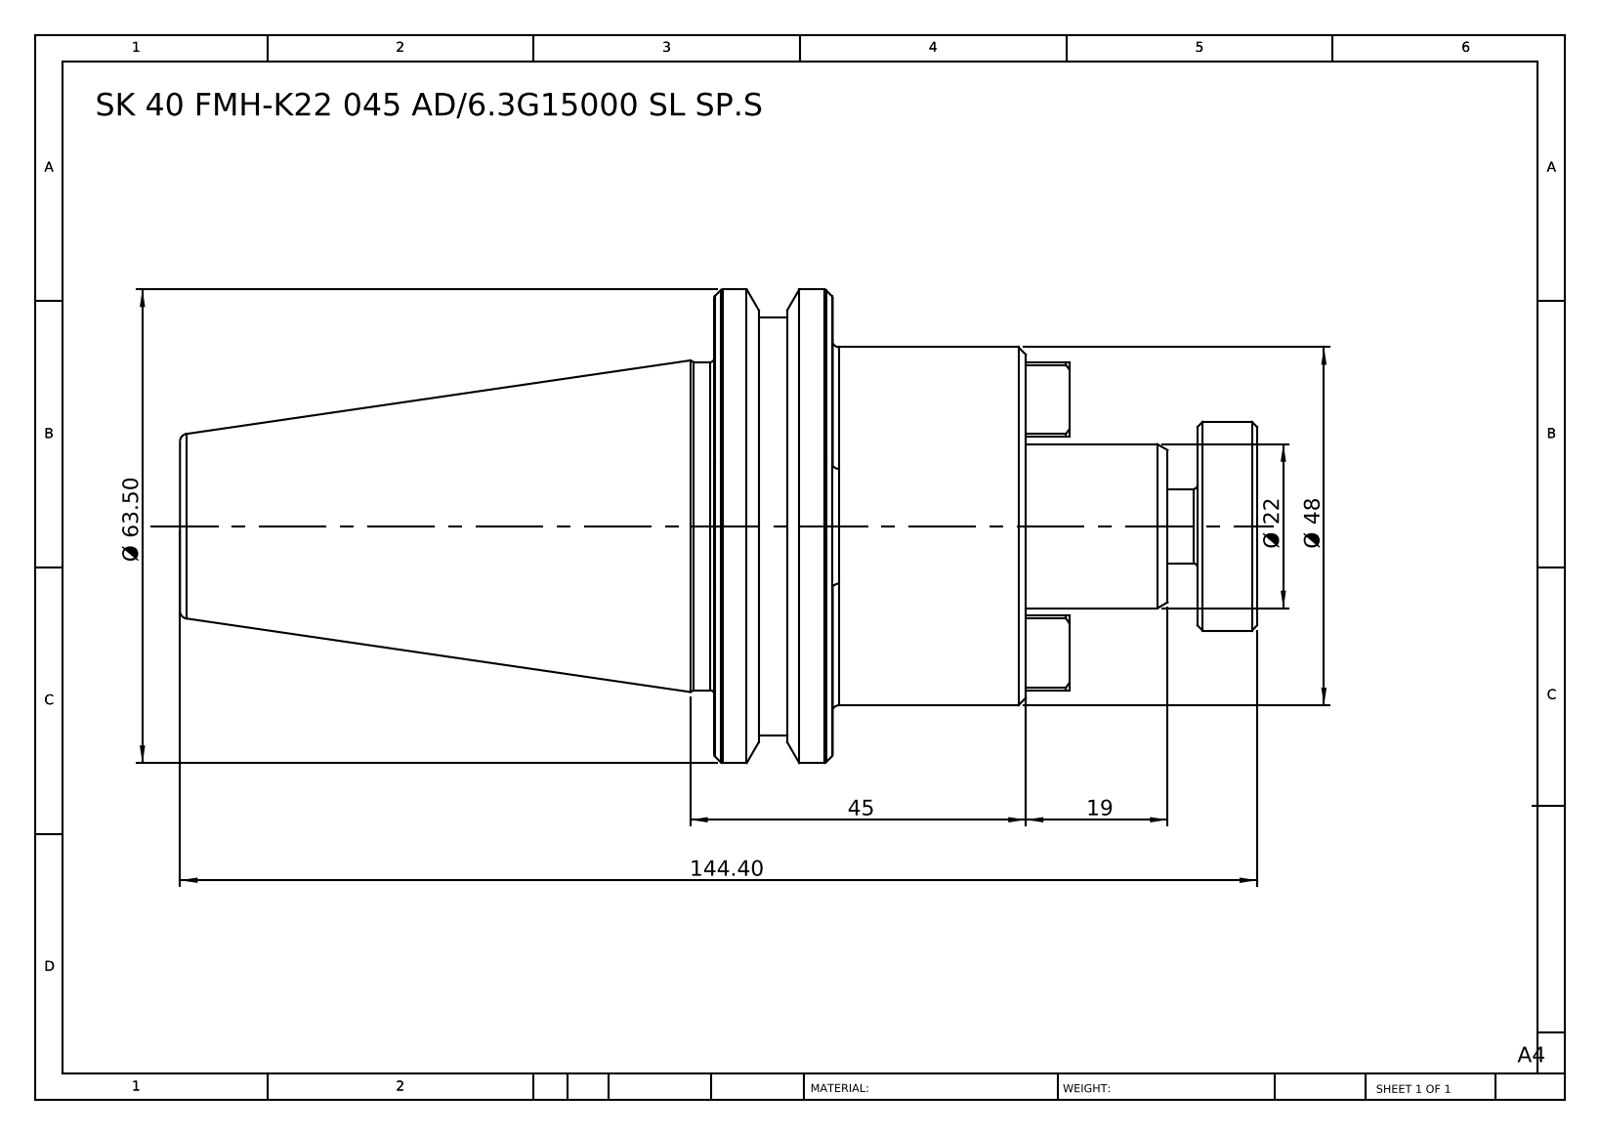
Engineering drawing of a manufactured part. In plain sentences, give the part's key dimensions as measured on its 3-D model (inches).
The part is named "SK40 FMH-K22 045 AD+B-6.3G15000 SL SP". Its 3-D file was written by "SolidWorks 2014 (CONFIG_CONTROL_DESIGN)". It is 1 solid with 103 faces: 35 planar, 16 cylindrical and 52 other. Overall it measures 5.685 by 2.5 by 2.5 inches. Its volume is 10.83 cubic inches and its surface area 37.57 square inches. Round bosses or shafts: 1 of diameter 2.5, 1 of diameter 2.205, 1 of diameter 1.89, 1 of diameter 1.732, 1 of diameter 1.102, 1 of diameter 0.866, 1 of diameter 0.394. The main face-to-face distances are 1.646, 1.02, 0.626, 1.22, 2.24, 2.866, 0.315, 0.906, 1.925, 2.551.
